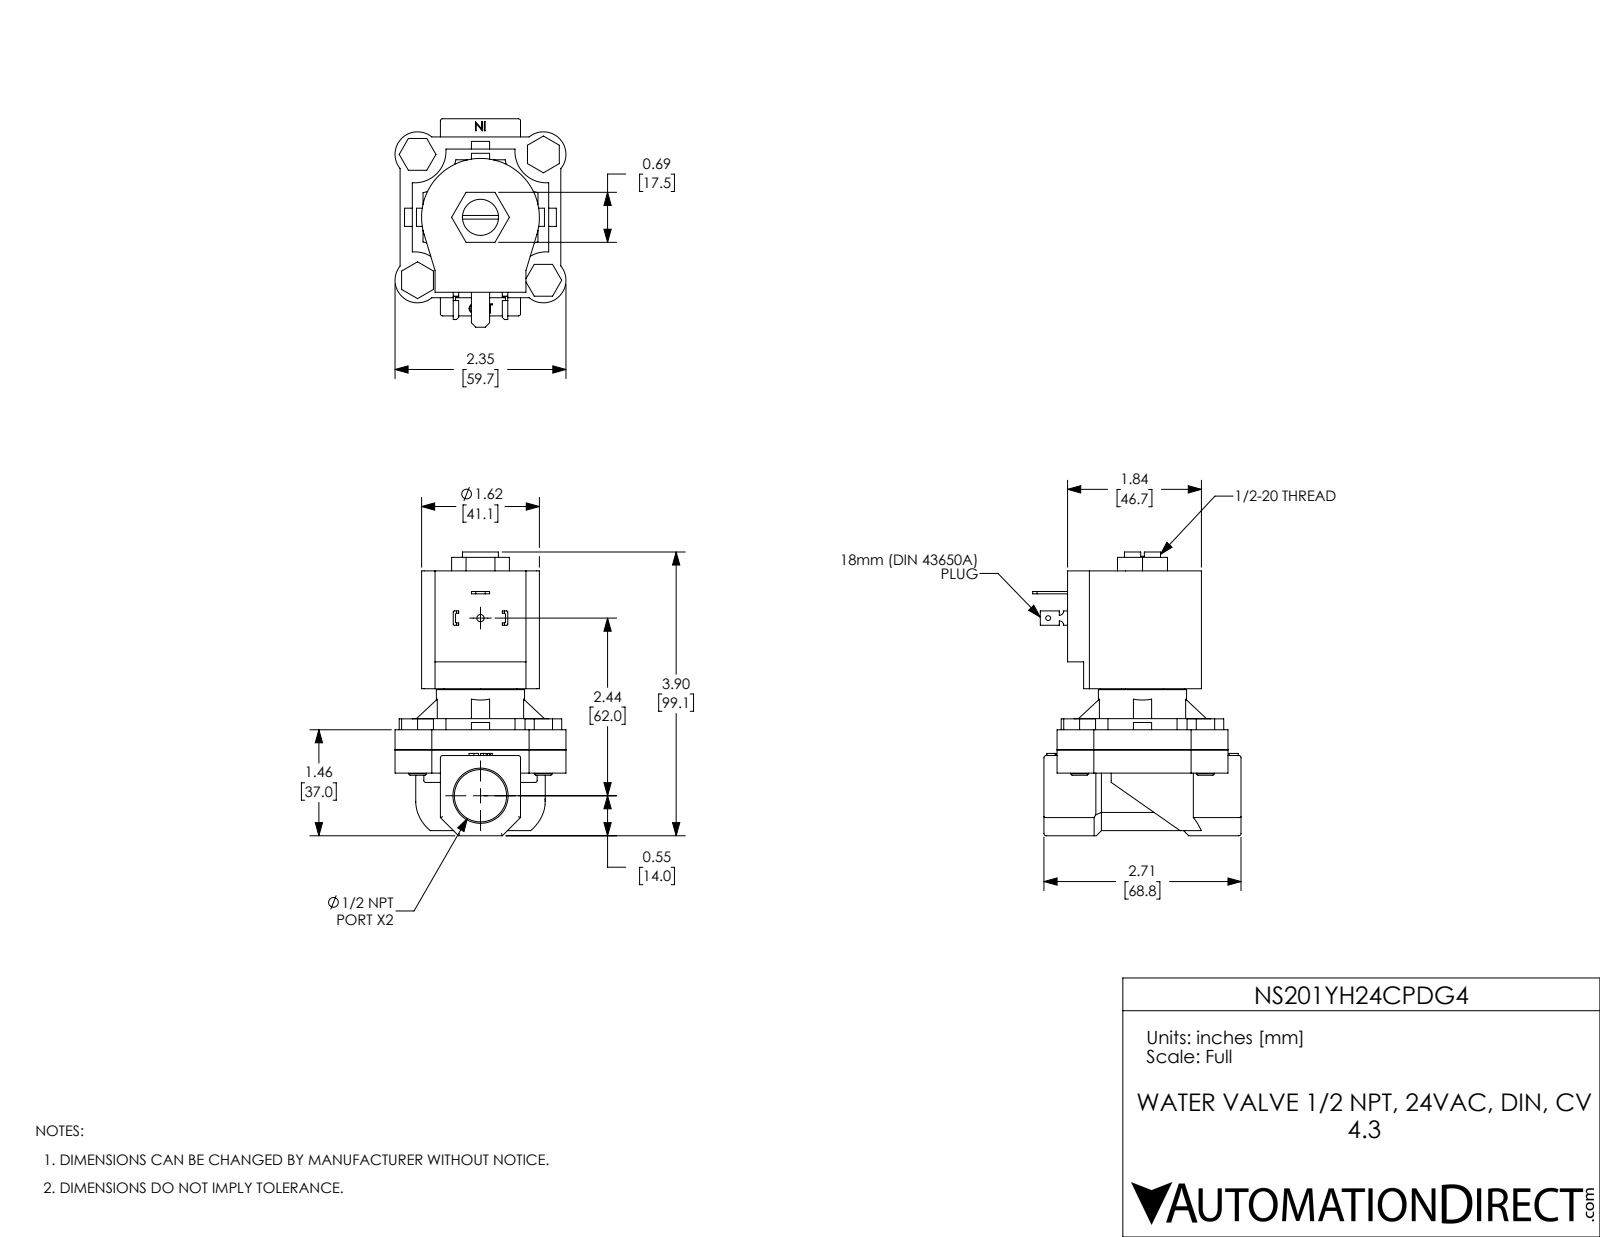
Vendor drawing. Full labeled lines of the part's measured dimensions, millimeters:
Part name (STEP PRODUCT): NS201YH24CPDG4
STEP written by: SolidWorks 2024 (CONFIG_CONTROL_DESIGN)
Units: millimetres
Bodies: 11 solids, 385 faces (239 planar, 113 cylindrical, 33 other)
Overall size (bounding box): 99.1 × 72.8 × 59.7
Volume: 165 000 mm³ · Surface area: 43 540 mm²
Round holes (diameter × count): ⌀6.4 ×4, ⌀1.7 ×1, ⌀2.5 ×1, ⌀12.6 ×1, ⌀13 ×1, ⌀18.3 ×1, ⌀29.3 ×1
Round bosses / shafts (diameter × count): ⌀6.3 ×4, ⌀30.8 ×1
Partial cylindrical surfaces — rounded edges, fillets, slot ends (radius × count): R0.8 ×15, R0.4 ×8, R7.9 ×4, R11 ×4, R14.7 ×4, R1.5 ×2, R20.6 ×1, R22.6 ×1
Main face-to-face distances: 7, 62.5, 55.4, 8.1, 15.1, 70.6, 14.1, 42.1, 6.4, 28
Hole centre spacings: 31.1, 43.9, 62.1, 62
